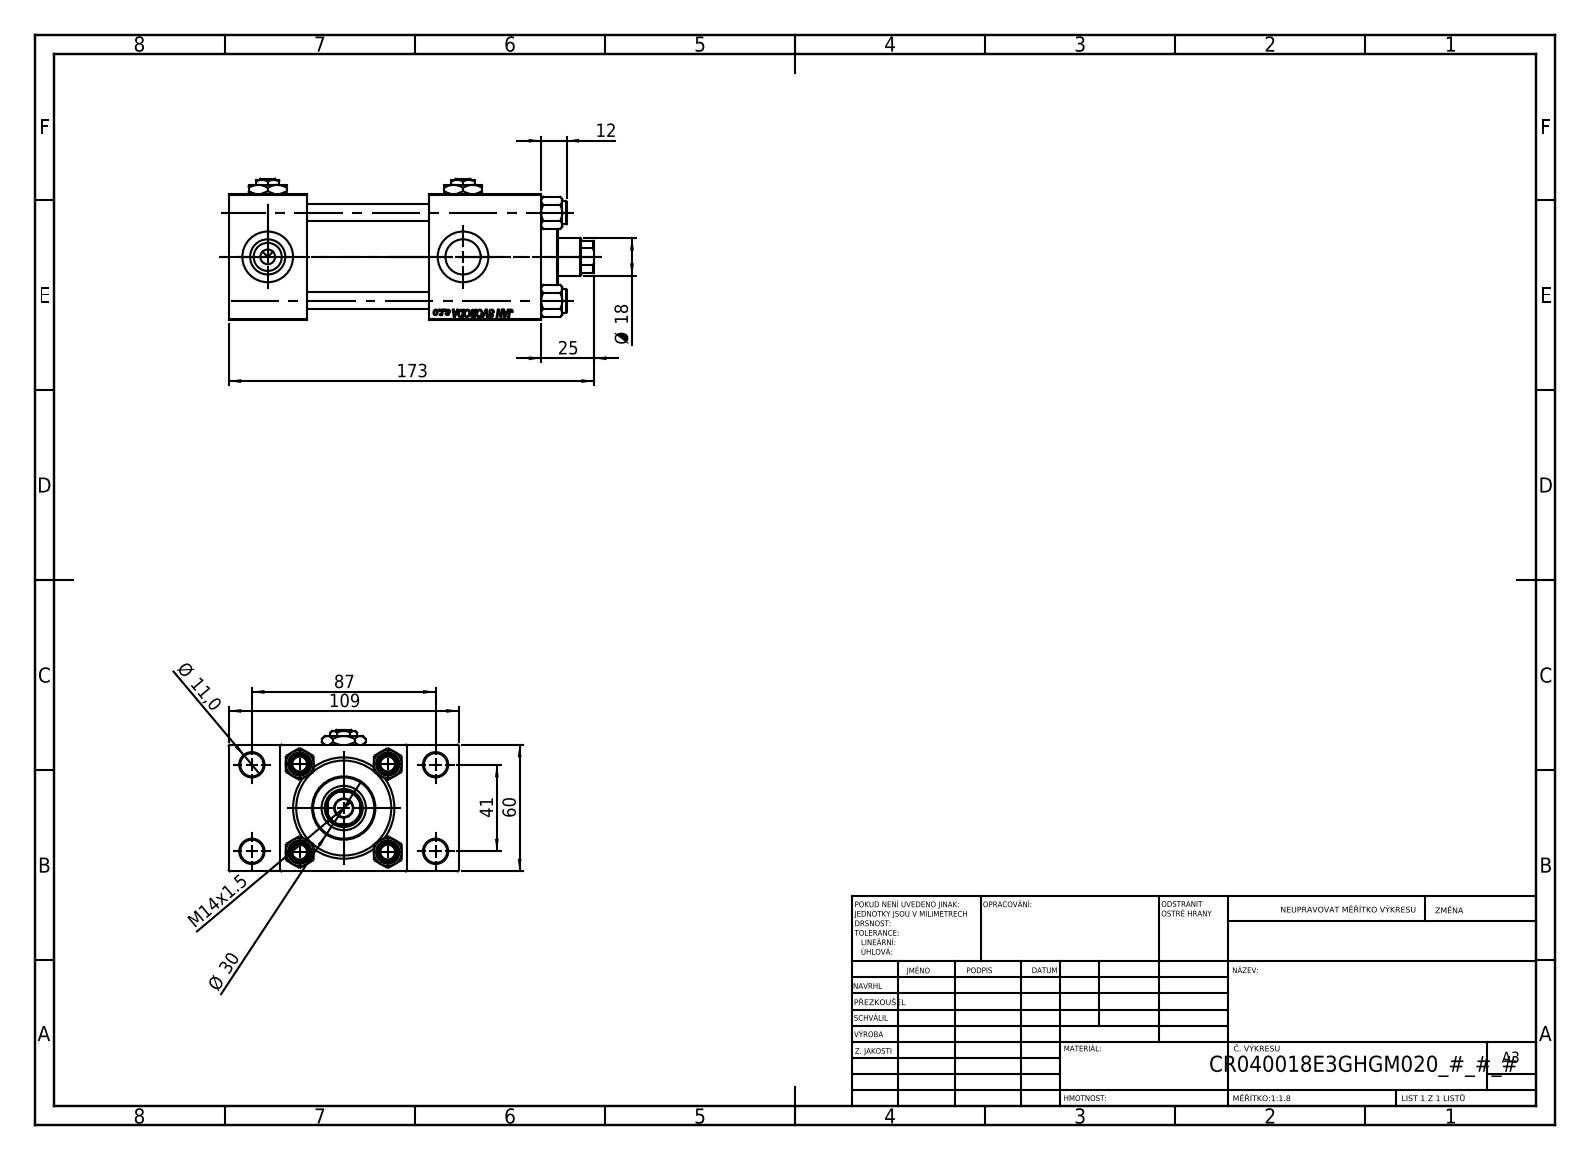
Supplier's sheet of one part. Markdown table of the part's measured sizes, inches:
| quantity | value |
| --- | --- |
| part name | V215CR_TYCINKA_E; NUT_M5_E; V215CR_VCP_E; Zatka_pro_OIL_PORT (+2 more) |
| STEP written by | SolidWorks 2019 (CONFIG_CONTROL_DESIGN) |
| units | inches |
| bodies | 13 solids, 1237 faces (546 planar, 97 cylindrical, 594 other) |
| overall size | 6.811 × 4.291 × 2.638 |
| volume | 30.26 in³ |
| surface area | 197.6 in² |
| round holes (diameter × count) | 0.315 × 4, 0.433 × 4, 0.656 × 4, 0.945 × 4, 0.276 × 3, 0.335 × 1, 0.709 × 1, 0.827 × 1, 1.22 × 1, 1.575 × 1, 1.772 × 1 |
| round bosses / shafts (diameter × count) | 0.433 × 4, 1.811 × 1, 1.181 × 1 |
| partial cylindrical surfaces (radius × count) | 0.335 × 1 |
| main face-to-face distances | 2.362, 1.457, 0.965, 3.327, 5.827, 4.37, 0.957, 2.283, 2.087, 3.24 |
| hole center spacings | 0.892, 1.161, 1.642, 1.856, 1.893, 2.533, 3.011, 1.614 |
